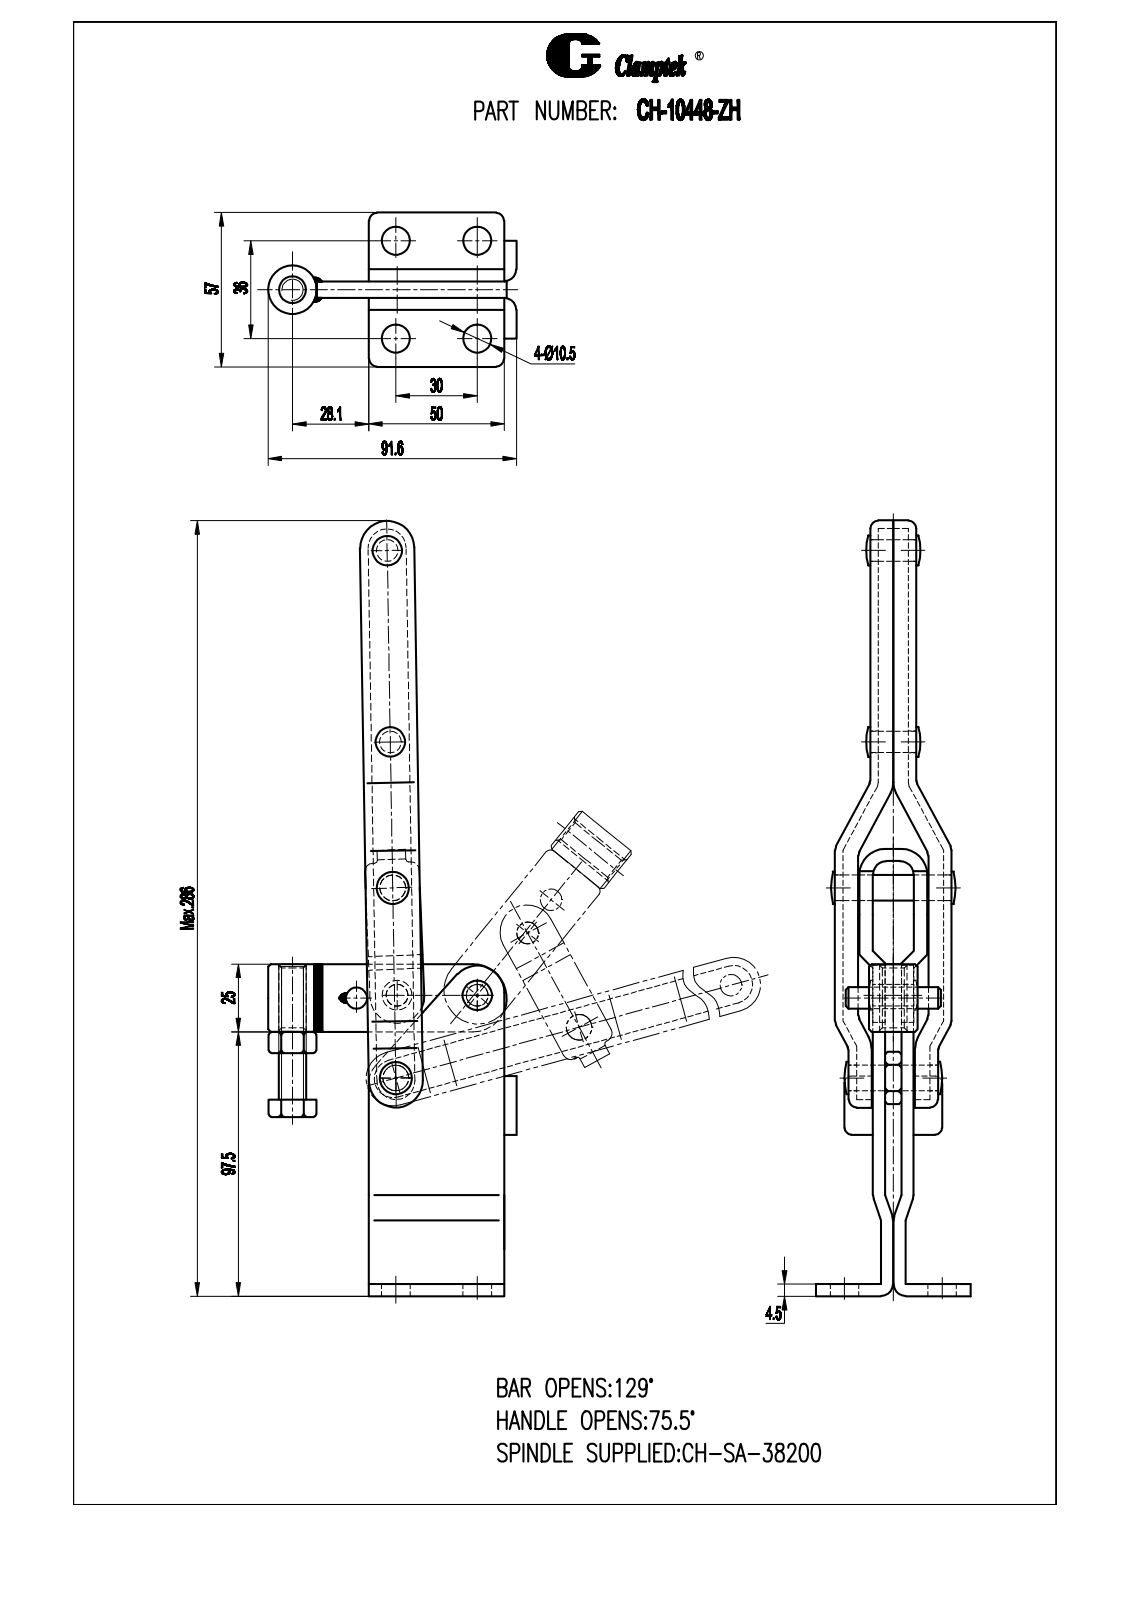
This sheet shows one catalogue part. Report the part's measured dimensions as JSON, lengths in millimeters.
{"part_name": "CH-10448-ZH", "step_written_by": "SolidWorks 2008 (CONFIG_CONTROL_DESIGN)", "units": "millimeters", "bodies": {"solids": 25, "faces": 931, "planar": 363, "cylindrical": 296, "other": 272}, "overall_size": [284.87, 91.48, 57], "volume_mm3": 140918, "surface_area_mm2": 86934, "round_holes": [[8, 5], [10.5, 4], [5.88, 2], [9.5, 2], [1.77, 1], [7.9, 1], [8.5, 1], [10, 1], [18, 1]], "round_bosses_or_shafts": [[7.9, 3], [11.9, 2], [9.4, 2], [16, 1], [14.4, 1], [13.4, 1], [10, 1], [1.54, 1]], "partial_cylinders_radius": [[3, 28], [4.5, 8], [8.5, 8], [2.5, 6], [2, 4], [4.5, 4], [5.5, 4], [7, 4]], "face_to_face_distances": [4.5, 3, 10.53, 17, 14, 13, 11, 5, 3.01, 7.51], "hole_center_spacings": [30, 36, 46.86, 14.99, 26.79, 29.54, 30.49, 32.86]}
